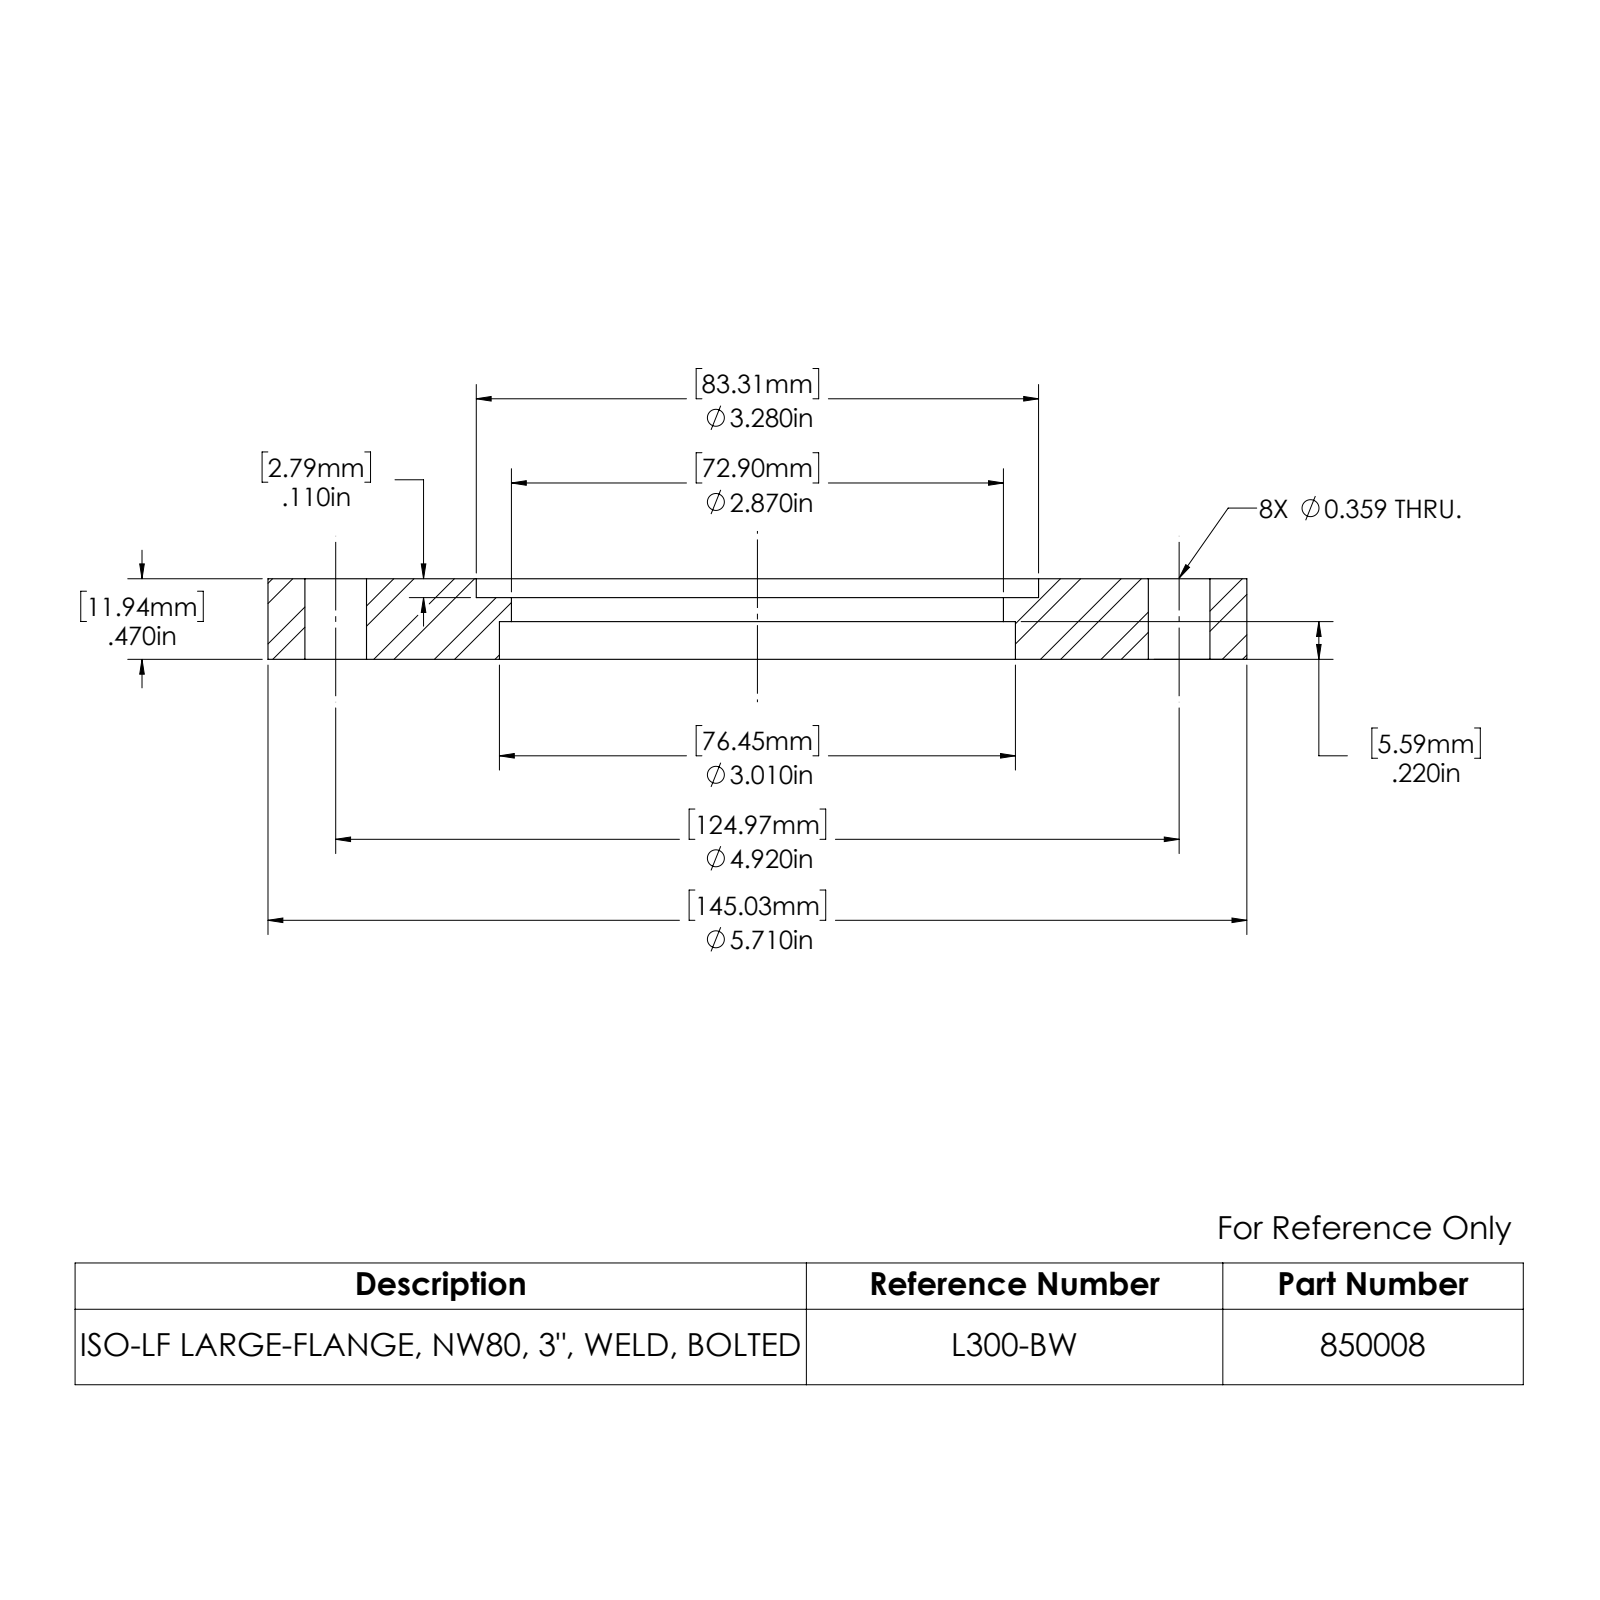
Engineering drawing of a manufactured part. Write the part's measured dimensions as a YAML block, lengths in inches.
part_name: "850008"
step_written_by: "SolidWorks 2022 (AUTOMOTIVE_DESIGN)"
units: inches
bodies: {solids: 1, faces: 28, planar: 4, cylindrical: 24, other: 0}
overall_size: [5.71, 5.71, 0.47]
volume: 8.253
surface_area: 53.81
round_holes:
  - {diameter: 0.359, count: 8}
  - {diameter: 2.87, count: 1}
  - {diameter: 3.01, count: 1}
  - {diameter: 3.28, count: 1}
round_bosses_or_shafts:
  - {diameter: 5.71, count: 1}
face_to_face_distances: [0.47, 0.36, 0.11, 0.22, 0.14, 0.25]
hole_center_spacings: [1.883, 2.46, 3.479, 4.545, 4.92]
